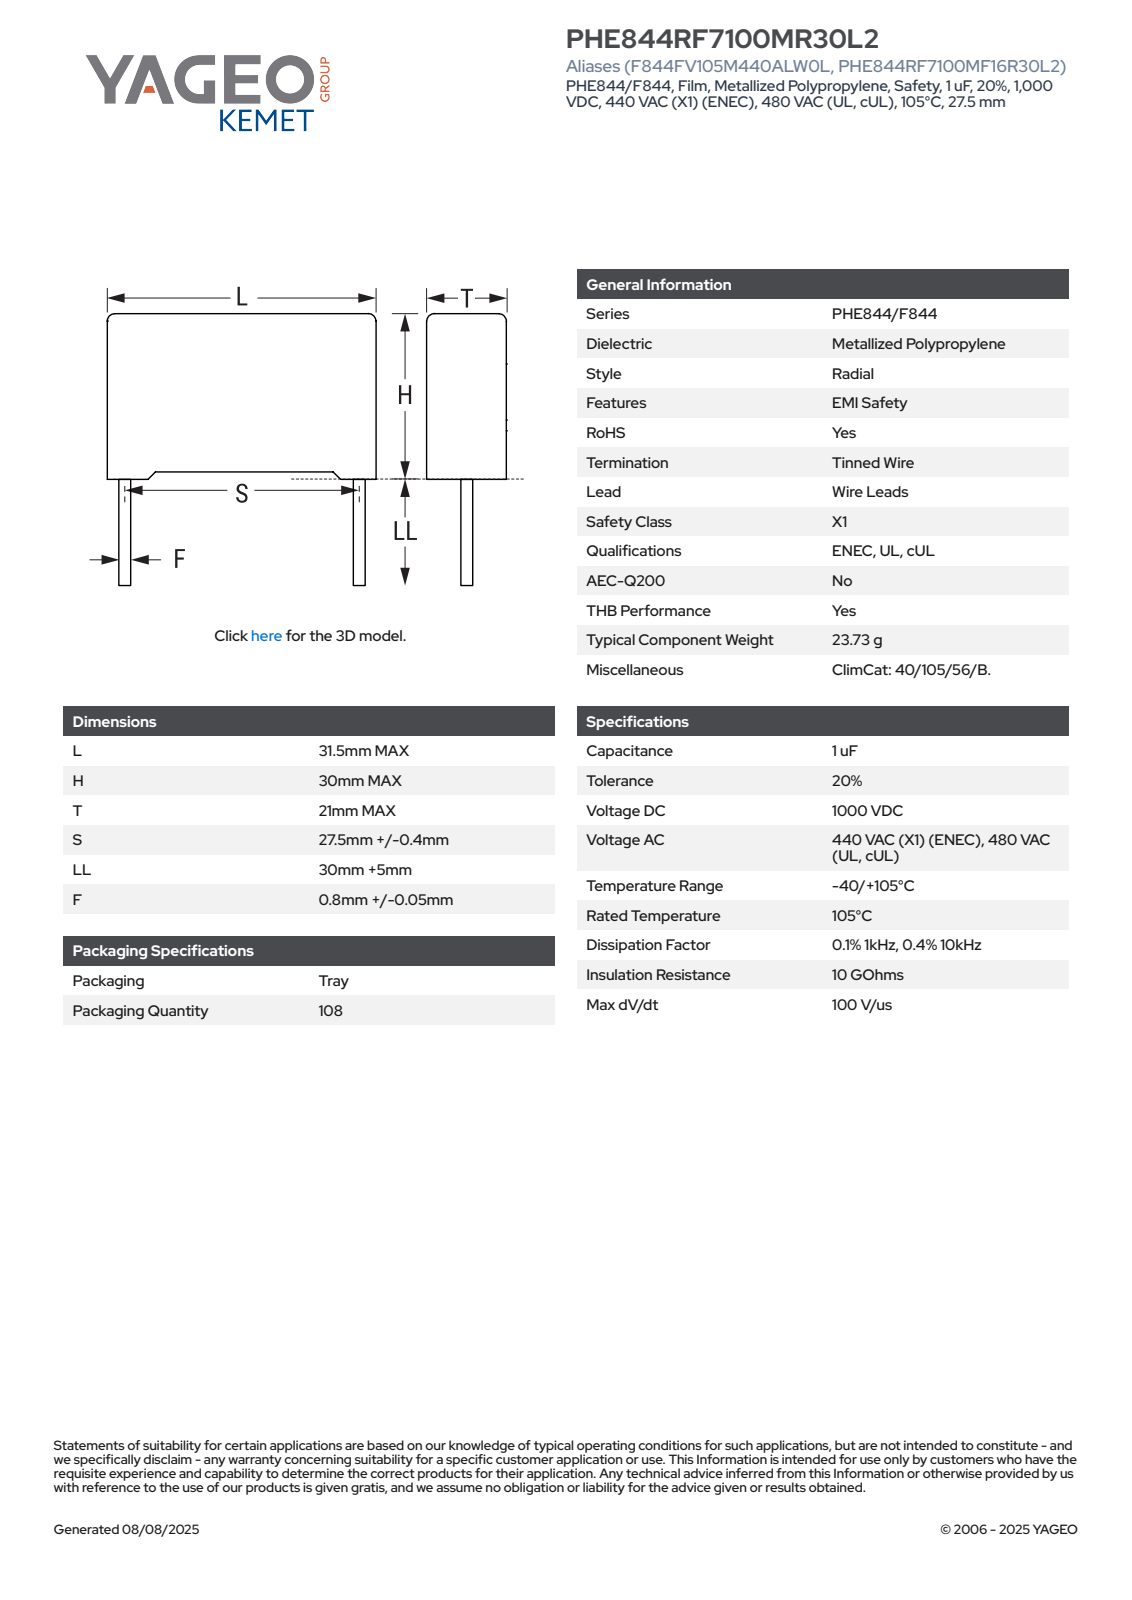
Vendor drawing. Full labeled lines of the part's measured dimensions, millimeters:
Part name (STEP PRODUCT): CFR_RB2_31.5X30X21_L31.5H30T21S27.5LL35F0.85
STEP written by: SolidWorks 2021 (AUTOMOTIVE_DESIGN)
Units: millimetres
Bodies: 4 solids, 85 faces (77 planar, 8 cylindrical, 0 other)
Overall size (bounding box): 65 × 31.5 × 21
Volume: 19 289 mm³ · Surface area: 4 710 mm²
Round bosses / shafts (diameter × count): ⌀0.85 ×2
Partial cylindrical surfaces — rounded edges, fillets, slot ends (radius × count): R0.5 ×4
Main face-to-face distances: 21, 31.5, 28.97, 29.25, 0.75, 1.03, 30, 1.05, 30.45, 21.01
